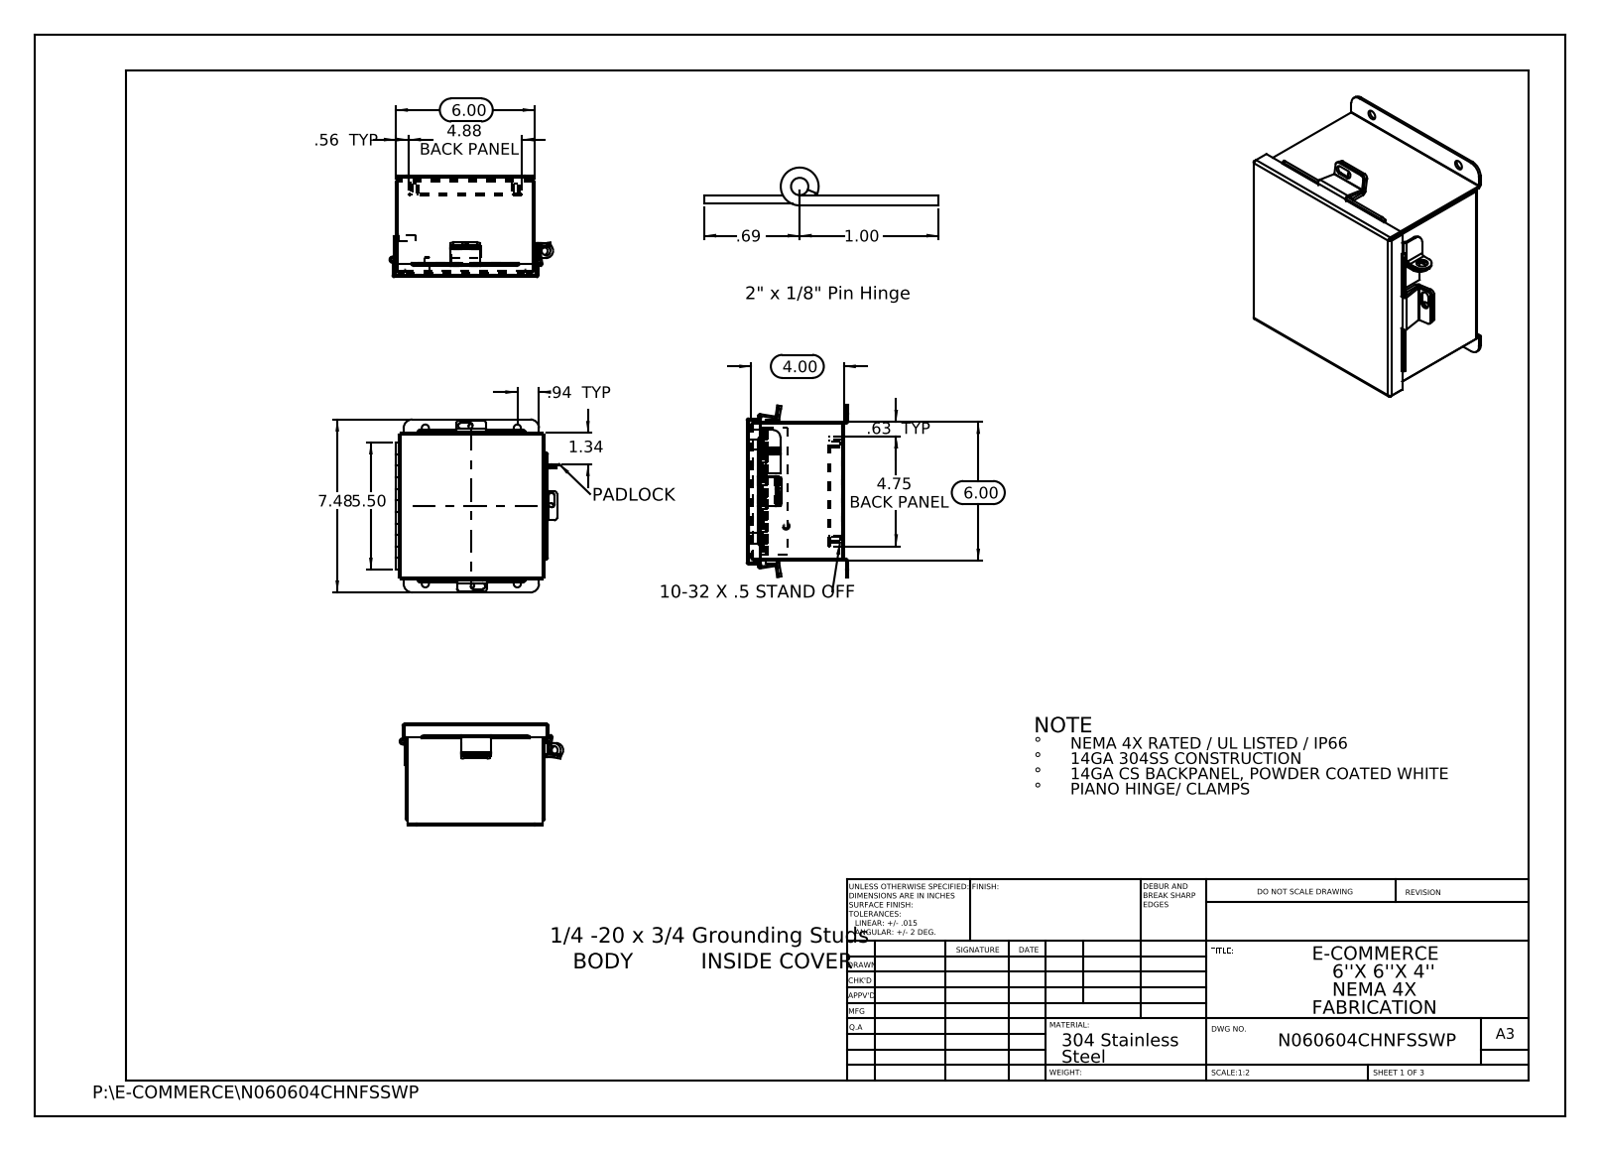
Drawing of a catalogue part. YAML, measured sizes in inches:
part_name: "N060604CHNFSSWP JIC_Cover_Template; N060604CHNFSSWP JIC Top; HW-CLH-JH-20104; N060604CHNFSSWP JIC Enclosure Template (+8 more)"
step_written_by: "SolidWorks 2013 (CONFIG_CONTROL_DESIGN)"
units: inches
bodies: {solids: 21, faces: 548, planar: 343, cylindrical: 185, other: 20}
overall_size: [7.476, 7.072, 4.39]
volume: 19.04
surface_area: 508.7
round_holes:
  - {diameter: 0.25, count: 7}
  - {diameter: 0.187, count: 4}
  - {diameter: 0.312, count: 4}
  - {diameter: 0.125, count: 1}
  - {diameter: 0.125, count: 1}
  - {diameter: 0.373, count: 1}
  - {diameter: 0.375, count: 1}
round_bosses_or_shafts:
  - {diameter: 0.313, count: 4}
  - {diameter: 0.315, count: 2}
  - {diameter: 0.236, count: 2}
  - {diameter: 0.273, count: 1}
  - {diameter: 0.25, count: 1}
partial_cylinders:
  - {radius: 0.013, count: 13}
  - {radius: 0.009, count: 12}
  - {radius: 0.088, count: 12}
  - {radius: 0.125, count: 10}
  - {radius: 0.083, count: 6}
  - {radius: 0.1, count: 6}
  - {radius: 0.133, count: 6}
  - {radius: 0.375, count: 4}
face_to_face_distances: [0.075, 5.925, 4.128, 5.85, 6, 4.053, 4.203, 0.104, 0.575, 0.5]
hole_center_spacings: [1.315, 4.373, 5.43, 6.846, 3.976, 4.126, 4.375, 6.013]
